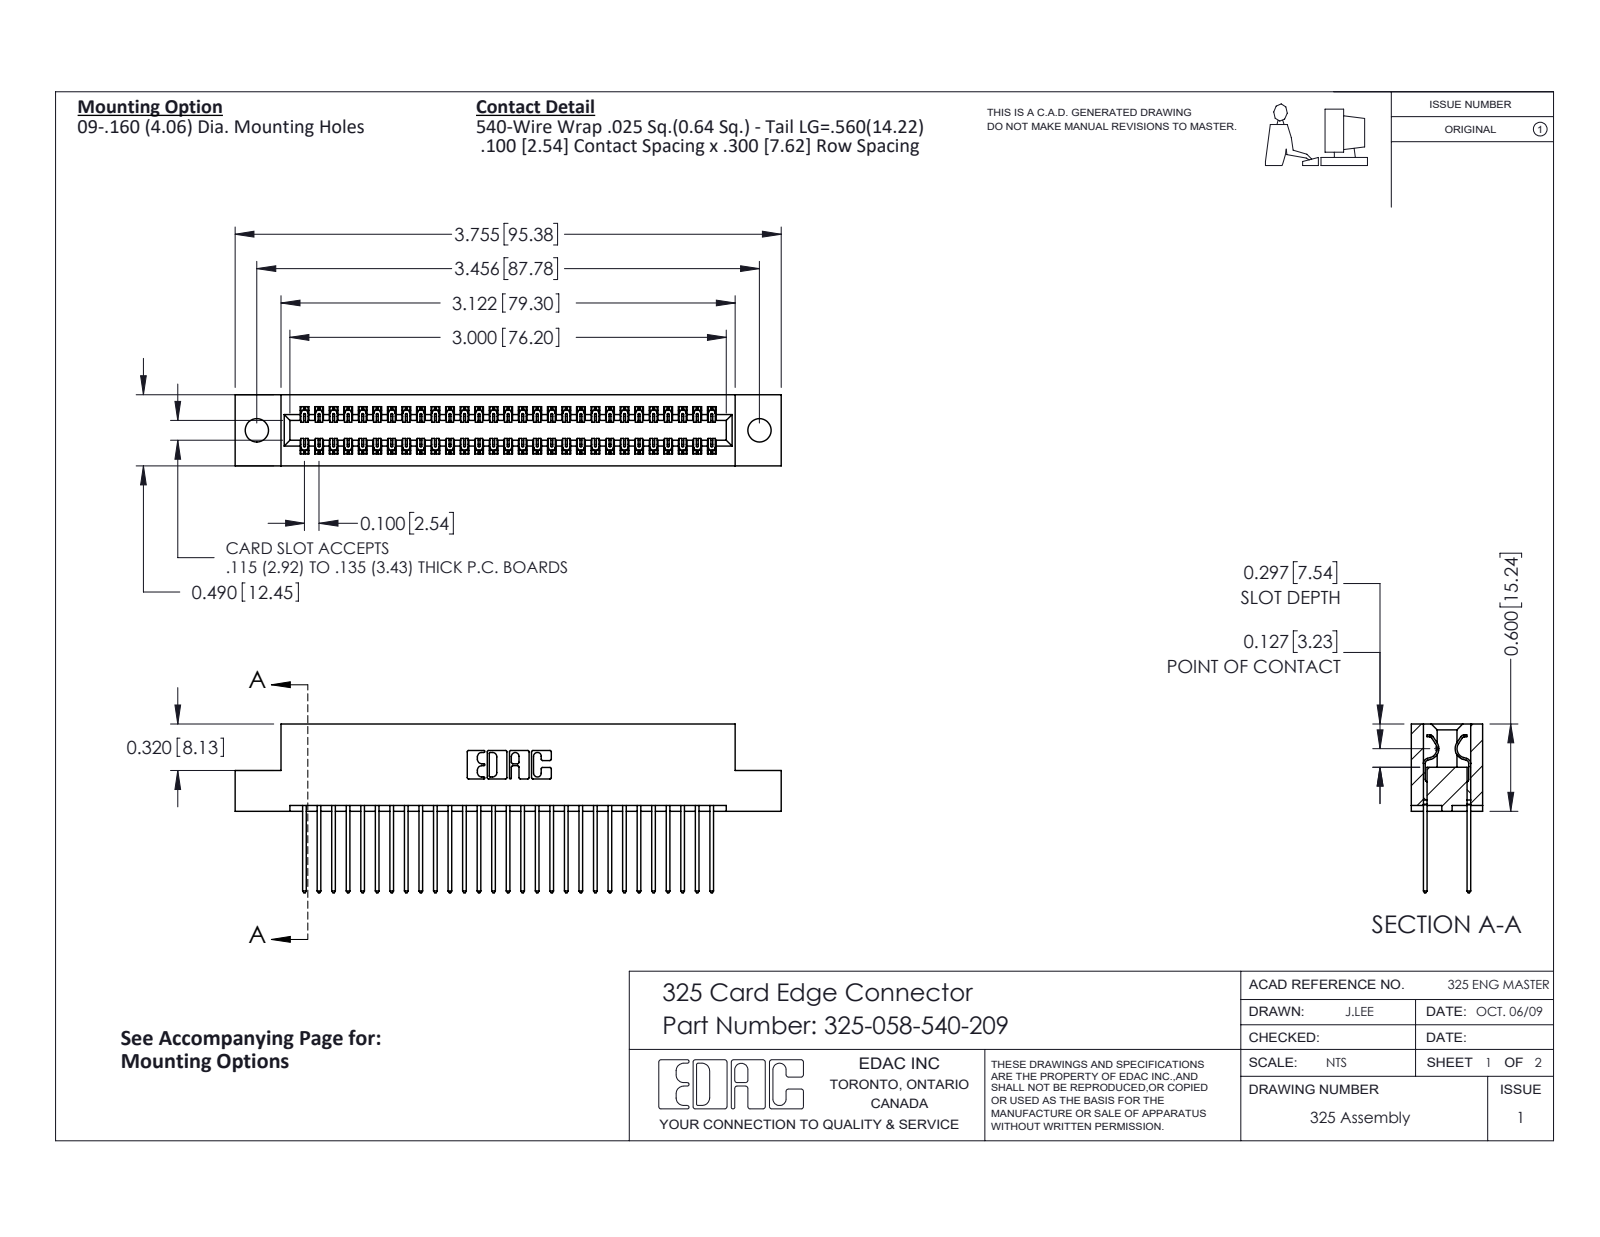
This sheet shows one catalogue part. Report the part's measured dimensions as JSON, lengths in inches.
{"part_name": "325-292-001_325-293-140; 325 Part_.160 TH; 325-058-540-209", "step_written_by": "SolidWorks 2016 (CONFIG_CONTROL_DESIGN)", "units": "inches", "bodies": {"solids": 59, "faces": 3130, "planar": 2158, "cylindrical": 972, "other": 0}, "overall_size": [3.755, 1.16, 0.49], "volume_in3": 0.744, "surface_area_in2": 23.88, "round_holes": [[0.16, 2]], "partial_cylinders_radius": [[0.006, 87], [0.01, 58], [0.01, 22], [0.007, 6], [0.031, 6], [0.026, 3], [0.014, 2], [0.022, 2]], "face_to_face_distances": [0.083, 0.407, 0.3, 0.107, 0.383, 0.025, 0.49, 0.325, 0.275, 0.04], "hole_center_spacings": [3.456]}
